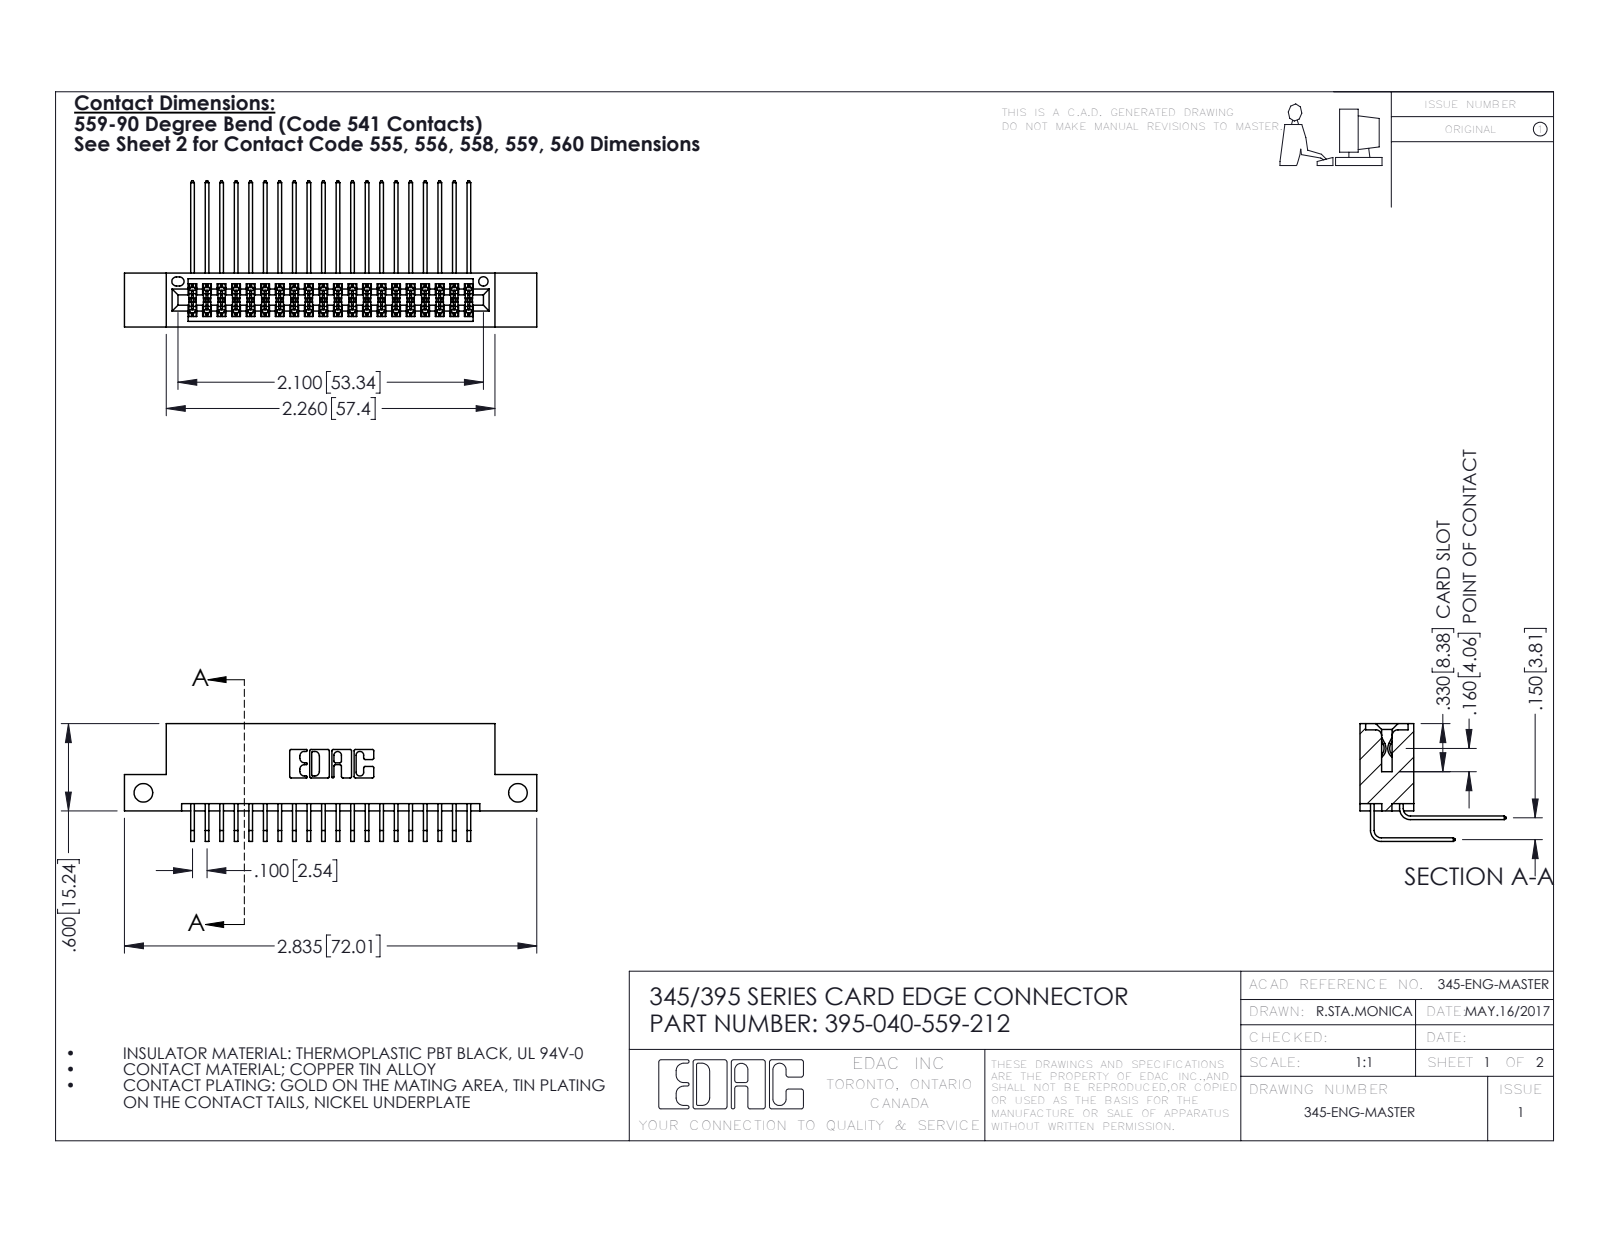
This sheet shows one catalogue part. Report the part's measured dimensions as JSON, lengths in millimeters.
{"part_name": "345-292-001_558 559 Tail - 1; 345 Part_Flush Mounting Lugs - Side Mount; 345-292-001_559 Tail - 2; 395-040-559-212", "step_written_by": "SolidWorks 2016 (CONFIG_CONTROL_DESIGN)", "units": "millimeters", "bodies": {"solids": 41, "faces": 2206, "planar": 1480, "cylindrical": 726, "other": 0}, "overall_size": [72, 25.5, 20.5], "volume_mm3": 6930, "surface_area_mm2": 10770, "round_holes": [[3.3, 2], [1.6, 1]], "partial_cylinders_radius": [[0.2, 61], [0.3, 22], [0.2, 6], [0.8, 6], [0.7, 3], [0.4, 2], [0.5, 2], [0.6, 2]], "face_to_face_distances": [1.8, 7.6, 5.1, 9.4, 2.5, 6.9, 0.6, 5.7, 3.8, 4.4], "hole_center_spacings": [65.4]}
